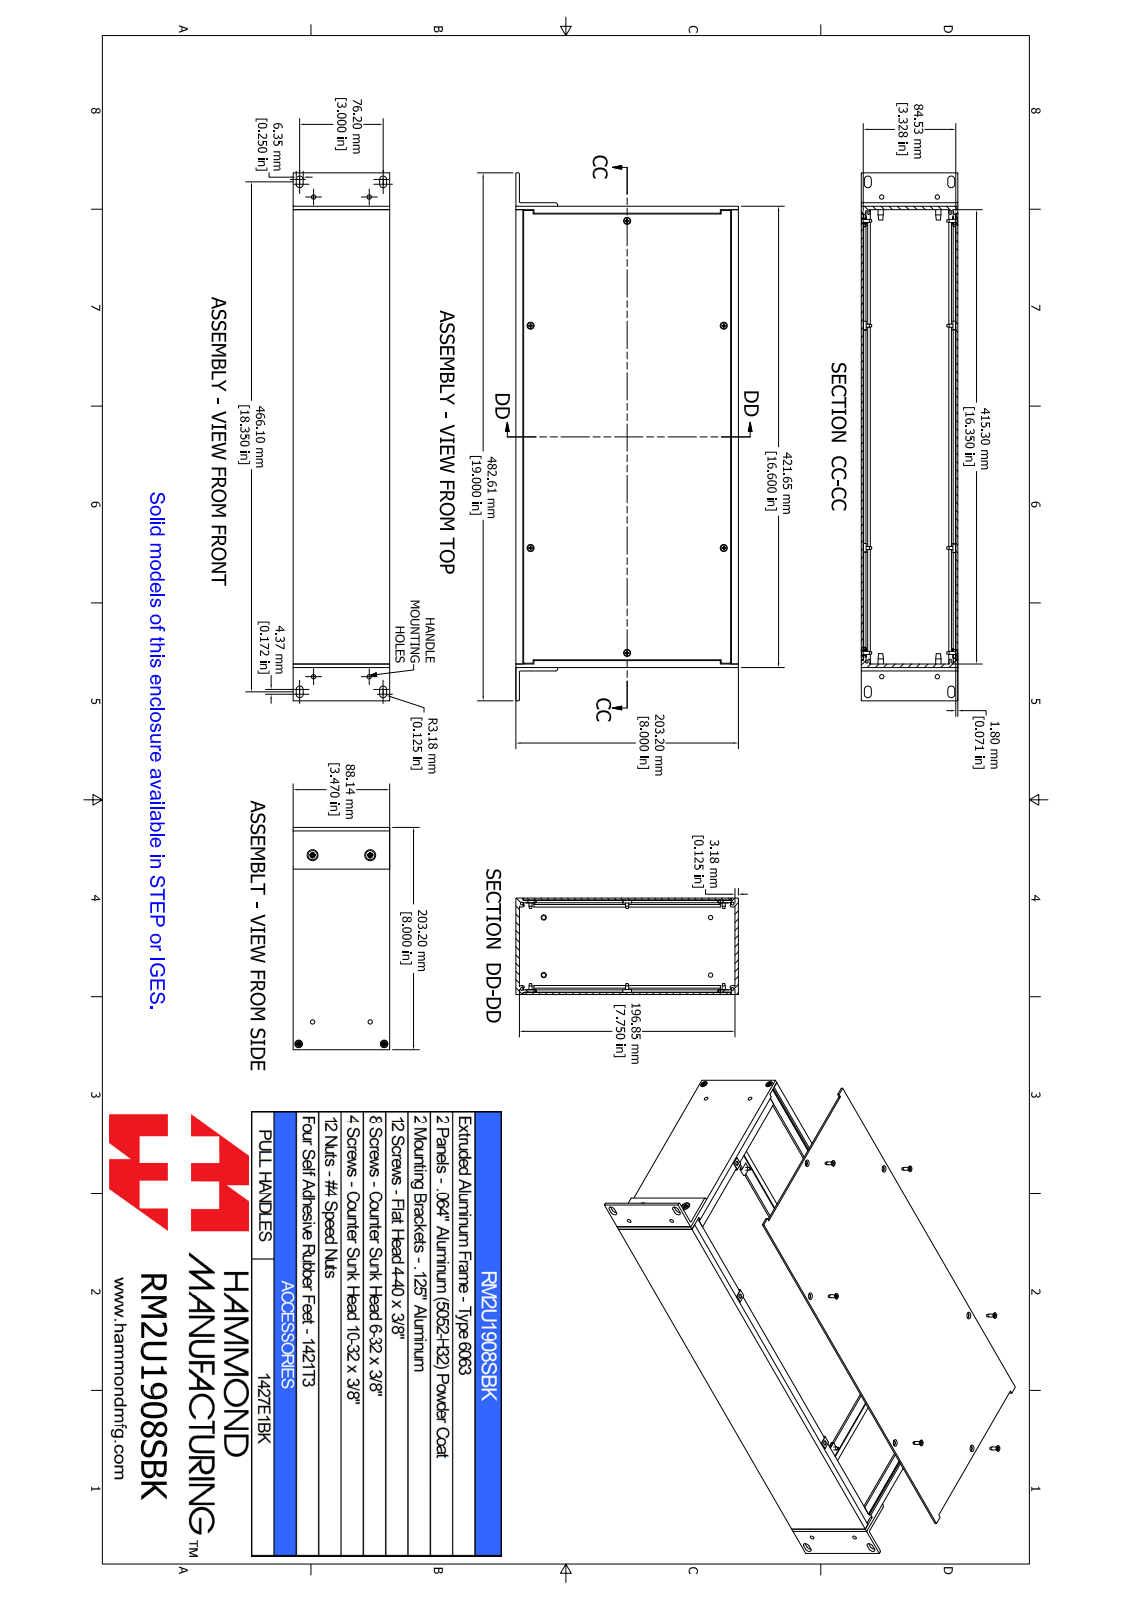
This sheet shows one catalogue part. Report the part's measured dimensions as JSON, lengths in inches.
{"part_name": "RM2U1908SBK", "step_written_by": "SolidWorks 2021 (AUTOMOTIVE_DESIGN)", "units": "inches", "bodies": {"solids": 44, "faces": 1182, "planar": 564, "cylindrical": 186, "other": 432}, "overall_size": [19, 8, 3.471], "volume_in3": 46.62, "surface_area_in2": 1014, "round_holes": [[0.098, 6], [0.157, 6], [0.169, 6], [0.138, 4], [0.156, 4], [0.157, 4], [0.197, 4]], "round_bosses_or_shafts": [[0.214, 6], [0.112, 6], [0.333, 4], [0.238, 4], [0.19, 4], [0.138, 4]], "partial_cylinders_radius": [[0.039, 18], [0.125, 16], [0.049, 12], [0.05, 8], [0.037, 6], [0.038, 4], [0.079, 2]], "face_to_face_distances": [0.071, 3.399, 3.47, 3.328, 0.125, 0.125, 8, 7.875, 7.75, 7.875], "hole_center_spacings": [6.809, 6, 7.261, 0.935, 0.935, 0.936, 2, 2.071]}
